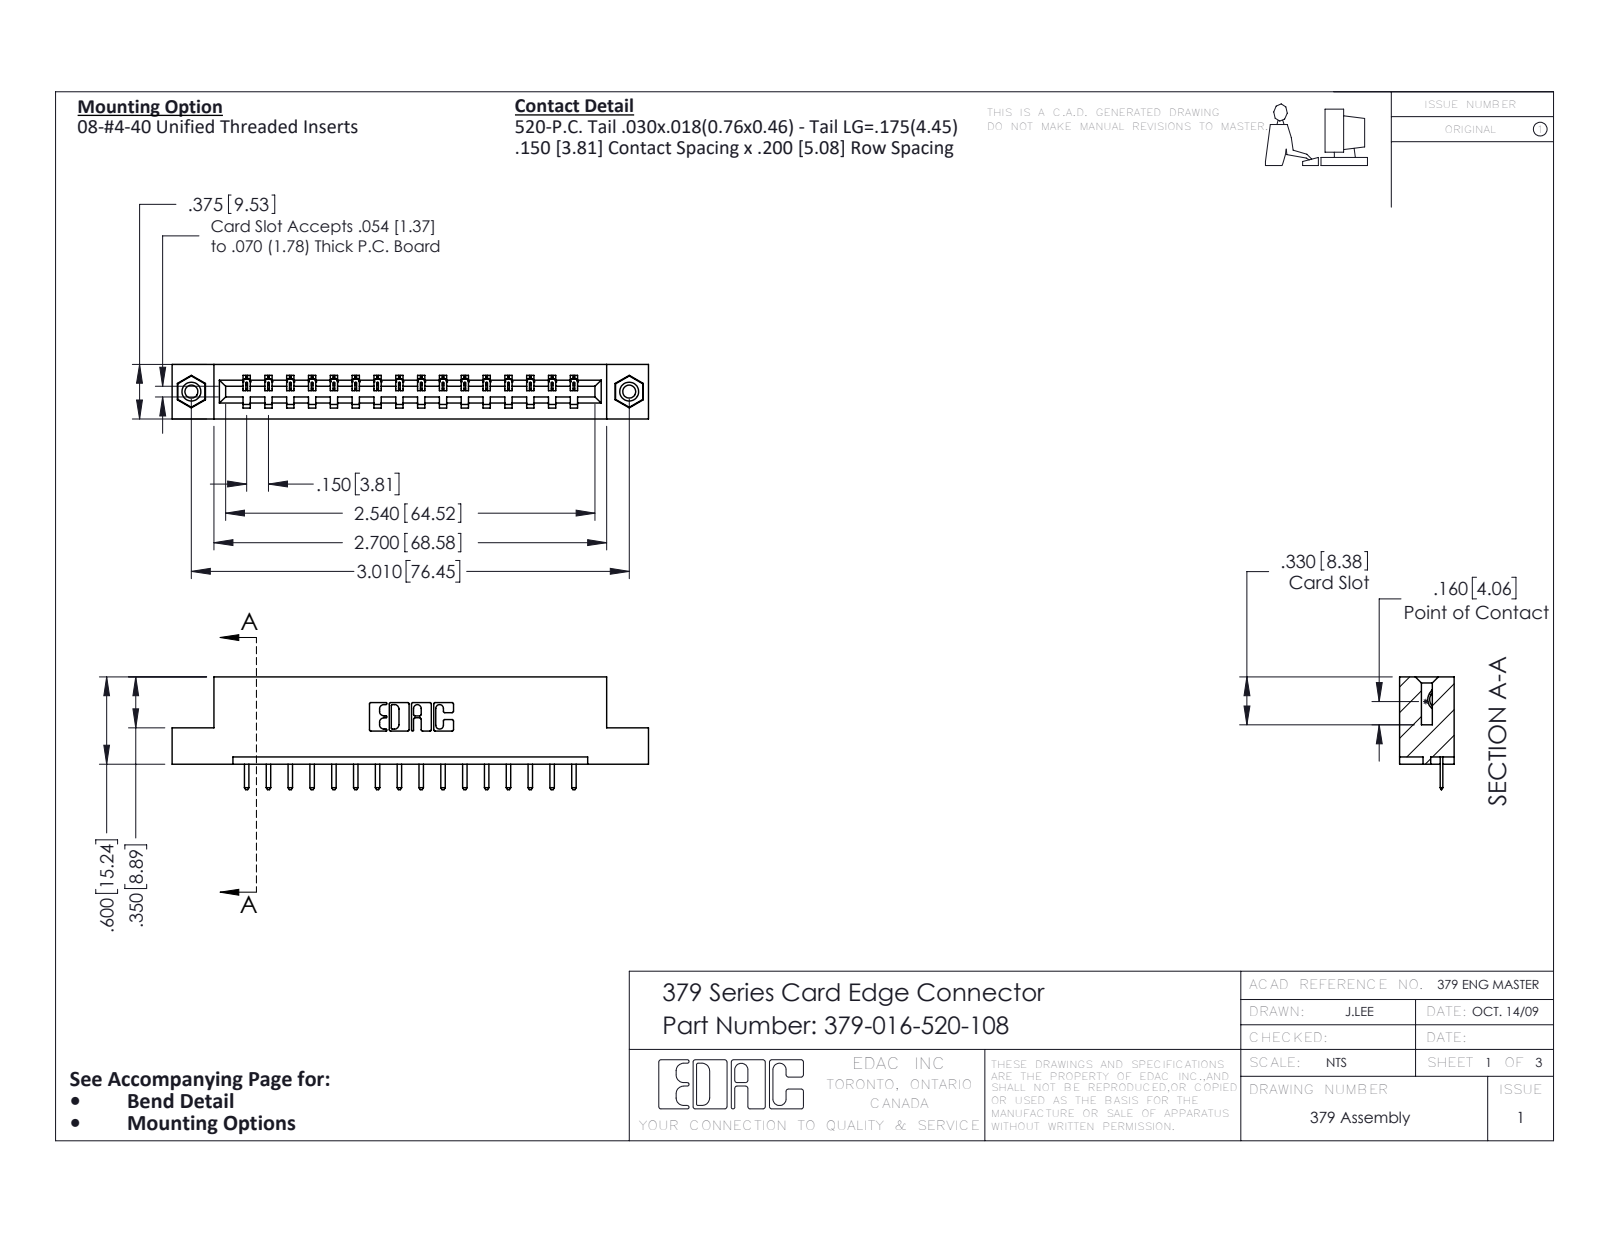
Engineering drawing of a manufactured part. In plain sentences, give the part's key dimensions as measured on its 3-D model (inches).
The part is named "379-016-520-108; 345-292-001_345-293-120; 345-250-001_345-250-003-102; 379 Part_Flush - .156 Dia - TI". Its 3-D file was written by "SolidWorks 2020 (CONFIG_CONTROL_DESIGN)". It is 19 solids with 1166 faces: 806 planar, 344 cylindrical and 16 other. Overall it measures 3.275 by 0.775 by 0.375 inches. Its volume is 0.511 cubic inches and its surface area 12.87 square inches. Round holes: 2 of diameter 0.089, 2 of diameter 0.125, 2 of diameter 0.156. Round bosses or shafts: 2 of diameter 0.155. Partial cylindrical surfaces (rounded edges, fillets, slot ends): 34 of radius 0.01, 32 of radius 0.006, 22 of radius 0.01, 6 of radius 0.007, 6 of radius 0.031, 3 of radius 0.026, 1 of radius 0.014, 1 of radius 0.022. The main face-to-face distances are 0.3, 0.375, 0.075, 0.6, 0.15, 0.225, 0.45, 0.75, 0.2, 0.9. The hole center spacings are 3.01.
